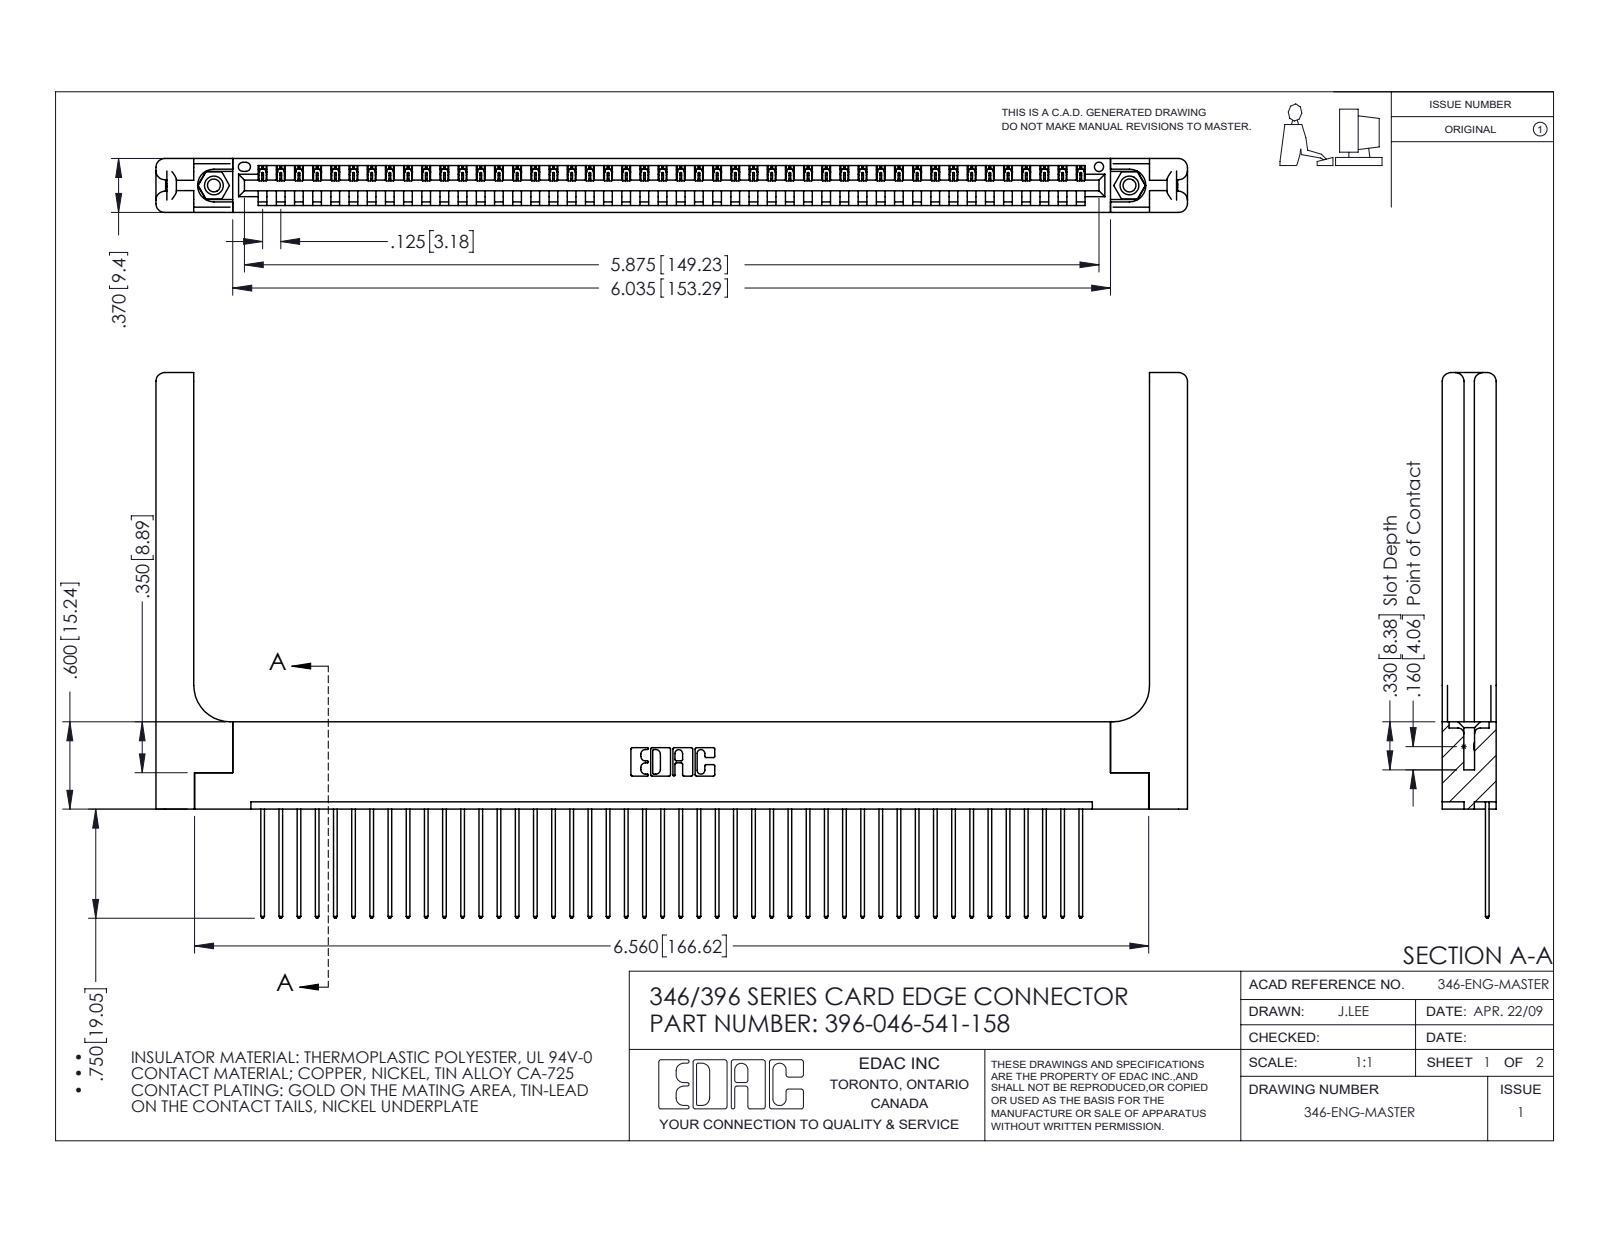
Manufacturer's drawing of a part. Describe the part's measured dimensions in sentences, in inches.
The part is named "346 Part_Flush Mounting Lugs - 0.156 Dia-TH; 346-220-058_345-220-058; 345-250-001_345-250-001-102; 345-292-001_345-293-141 (+1 more)". Its 3-D file was written by "SolidWorks 2016 (CONFIG_CONTROL_DESIGN)". It is 51 solids with 3046 faces: 2064 planar, 922 cylindrical and 60 other. Overall it measures 7.091 by 3.75 by 0.37 inches. Its volume is 1.522 cubic inches and its surface area 43.23 square inches. Round holes: 2 of diameter 0.089, 2 of diameter 0.125, 2 of diameter 0.156, 1 of diameter 0.064. Round bosses or shafts: 2 of diameter 0.155. Partial cylindrical surfaces (rounded edges, fillets, slot ends): 92 of radius 0.006, 92 of radius 0.01, 22 of radius 0.01, 16 of radius 0.06, 6 of radius 0.007, 6 of radius 0.031, 3 of radius 0.026, 2 of radius 0.03. The main face-to-face distances are 0.048, 0.322, 0.37, 0.072, 0.148, 0.15, 0.298, 0.025, 0.25, 0.222. The hole center spacings are 0.246, 6.086, 6.295.
